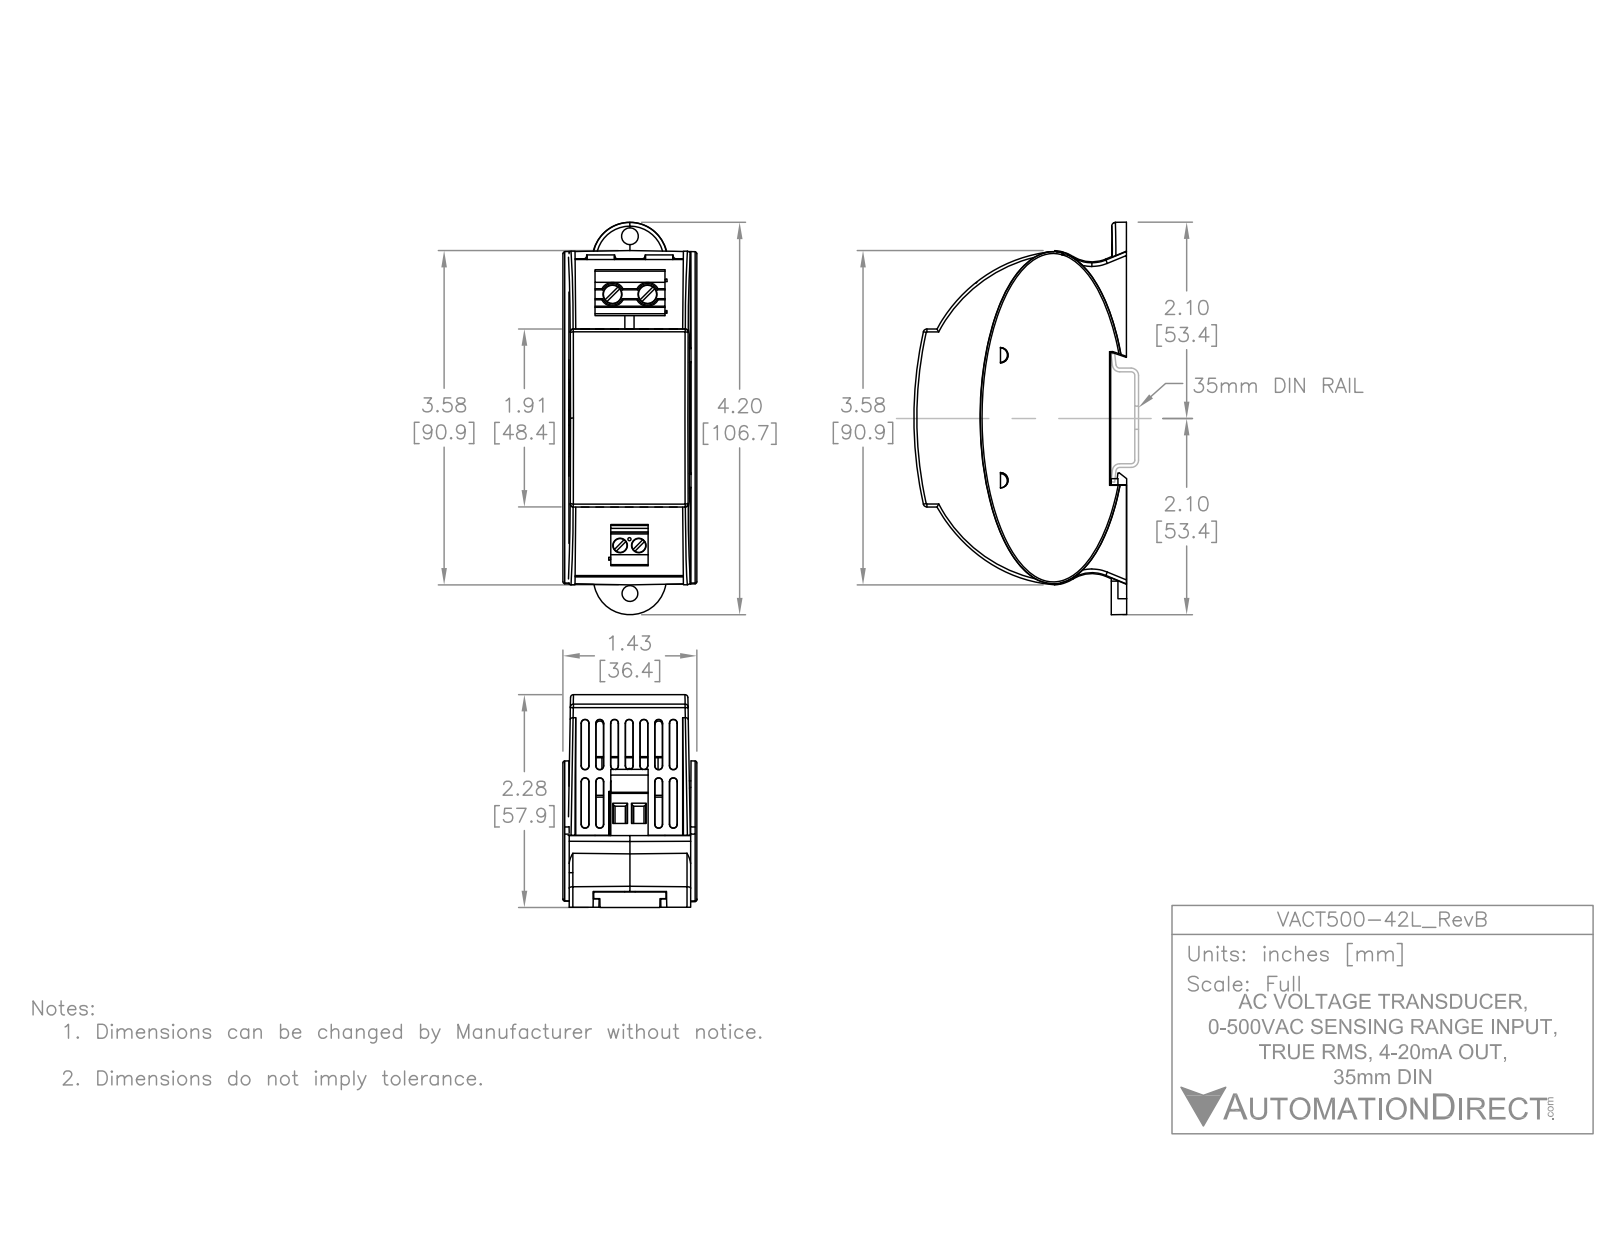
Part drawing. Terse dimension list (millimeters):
name: VACT500-42L
written by: SolidWorks 2021 (AUTOMOTIVE_DESIGN)
unit: mm
bodies: 6 solids, 755 faces (442 planar, 122 cylindrical, 191 other)
size: 106.8 × 58.4 × 37.1
volume: 50 550 mm³; area: 49 380 mm²
holes: 2× ⌀4, 2× ⌀5.2
bosses: 2× ⌀5, 2× ⌀3.8, 2× ⌀1.3, 2× ⌀0.5
rounds: 20× R0.2, 11× R0.5, 8× R0.2, 8× R0.7, 8× R1, 4× R0.3, 4× R0.8, 4× R1
face distances: 36.4, 1.6, 11.1, 12.7, 32.3, 31.9, 6.8, 17.8, 19.5, 48.4
hole spacings: 5.1, 9.5, 68.4, 68.4, 68.7, 68.7
